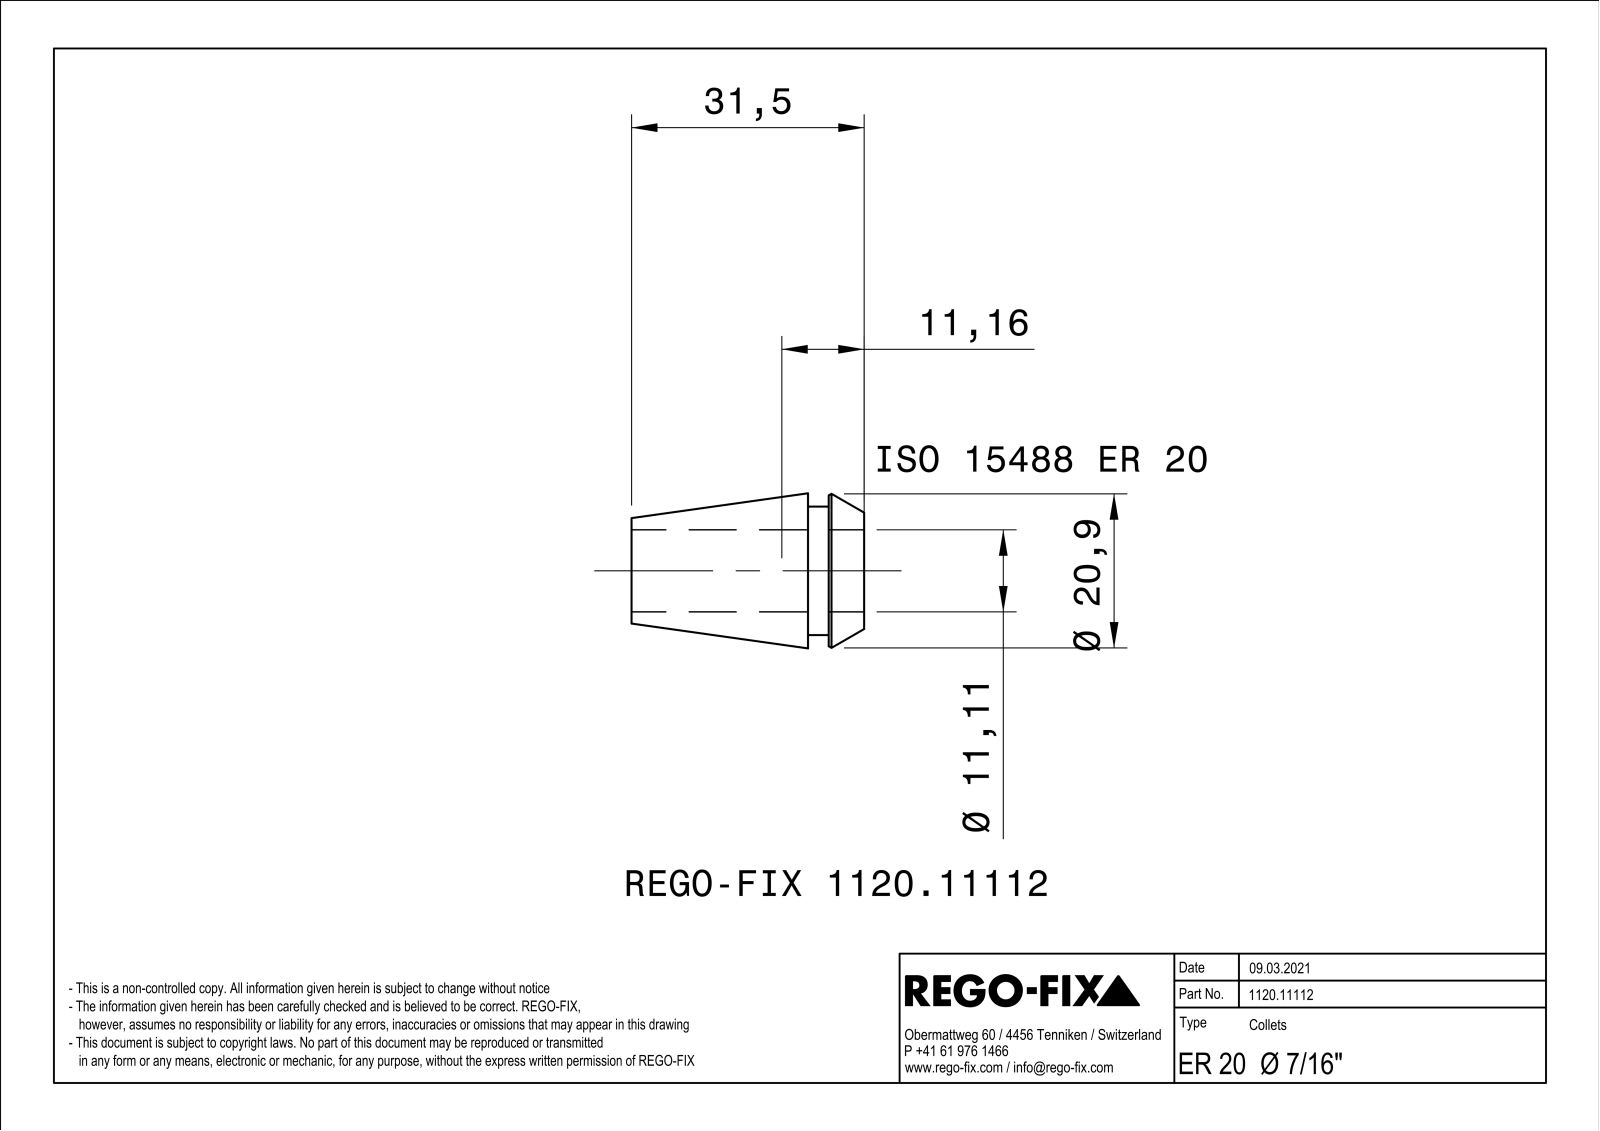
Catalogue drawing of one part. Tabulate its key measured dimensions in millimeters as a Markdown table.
| quantity | value |
| --- | --- |
| part name | NOCUT |
| STEP written by | SIEMENS PLM Software Solid Edge ST10 (AUTOMOTIVE_DESIGN) |
| units | millimeters |
| bodies | 1 solid, 177 faces (88 planar, 9 cylindrical, 80 other) |
| overall size | 31.5 × 20.99 × 20.99 |
| volume | 3 934 mm³ |
| surface area | 5 659 mm² |
| round holes (diameter × count) | 11.11 × 1 |
| round bosses / shafts (diameter × count) | 17.4 × 1 |
| main face-to-face distances | 0.6, 7.6, 4.8, 2.8, 31.5, 26.7, 23.9, 5.5, 0.7, 2.1 |
